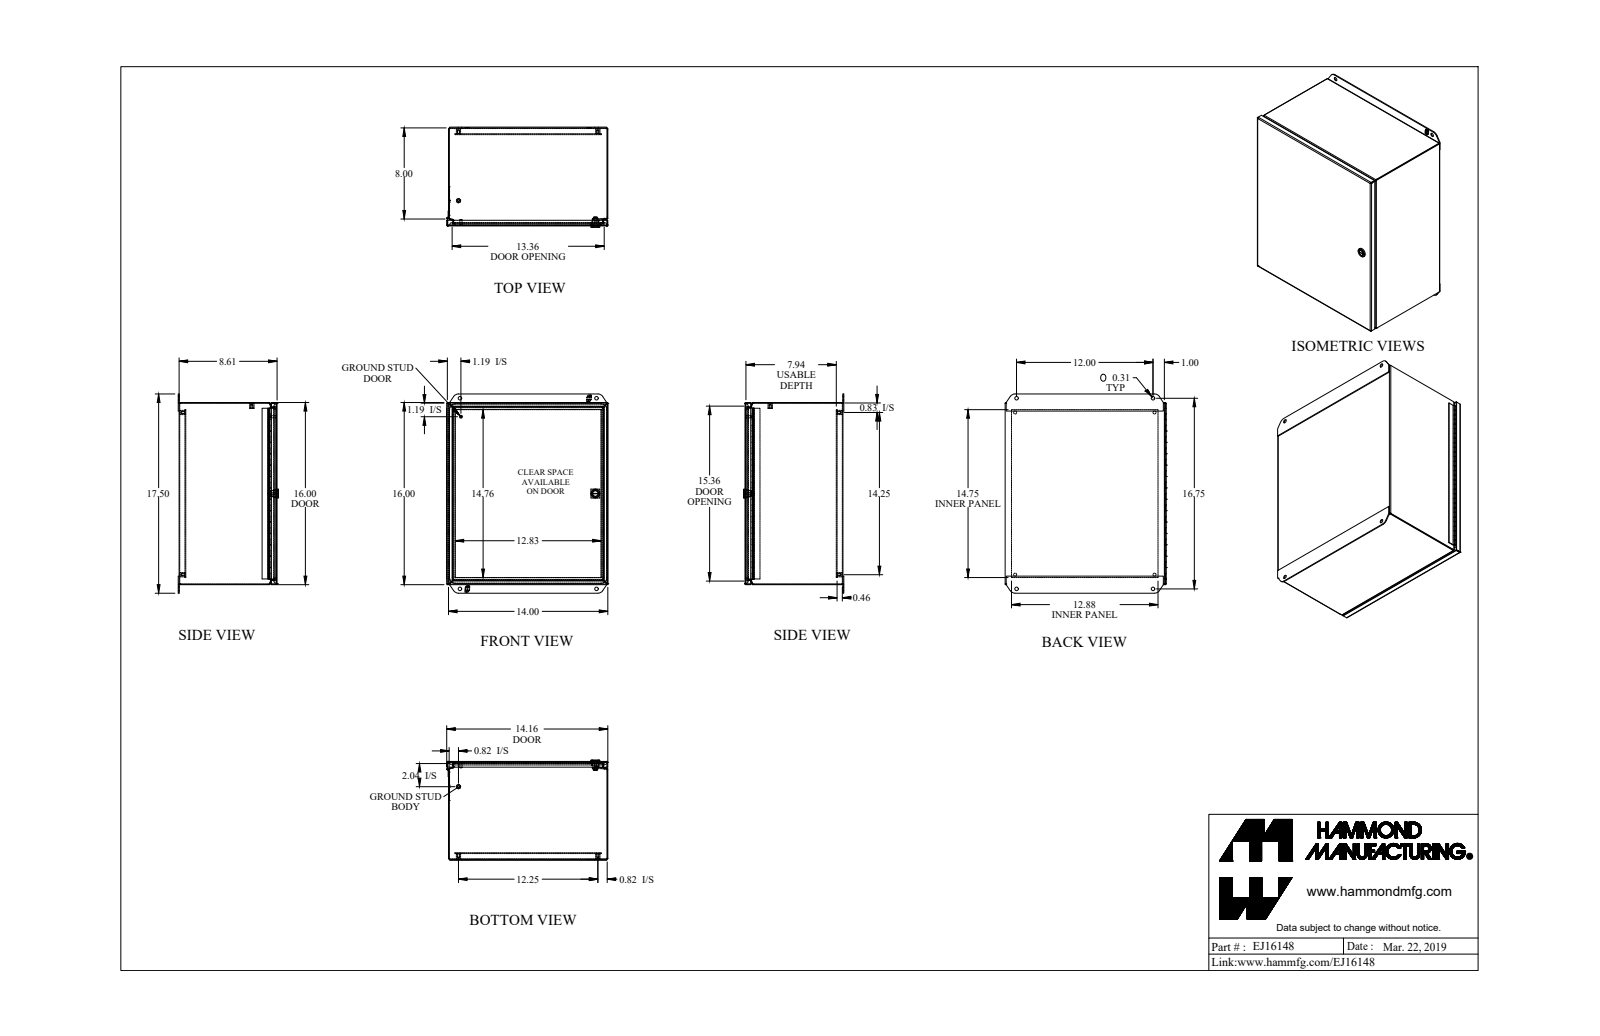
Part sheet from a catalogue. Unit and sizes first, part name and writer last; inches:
Units: inches
Overall size (bounding box): 17.5 × 14.165 × 8.805
Round holes (diameter × count): ⌀0.156 ×5, ⌀0.265 ×4, ⌀0.313 ×4, ⌀0.05 ×1, ⌀0.516 ×1
Round bosses / shafts (diameter × count): ⌀0.375 ×5, ⌀0.788 ×1, ⌀0.535 ×1, ⌀0.496 ×1, ⌀0.435 ×1, ⌀0.25 ×1, ⌀0.188 ×1, ⌀0.1 ×1
Partial cylindrical surfaces — rounded edges, fillets, slot ends (radius × count): R0.029 ×16, R0.086 ×16, R0.281 ×10, R0.25 ×4, R0.499 ×4, R0.5 ×4, R0.06 ×2, R0.539 ×2
Main face-to-face distances: 0.057, 8.554, 13.943, 0.072, 0.589, 15.943, 8.611, 8.497, 0.46, 0.517
Hole centre spacings: 1.256, 15.5, 19.679, 14.25, 12.189, 7.128, 8.375, 12
Volume: 79.66 in³ · Surface area: 2 641 in²
Bodies: 16 solids, 771 faces (425 planar, 254 cylindrical, 92 other)
Part name (STEP PRODUCT): EJ16148_Default
STEP written by: SolidWorks 2019 (CONFIG_CONTROL_DESIGN)
